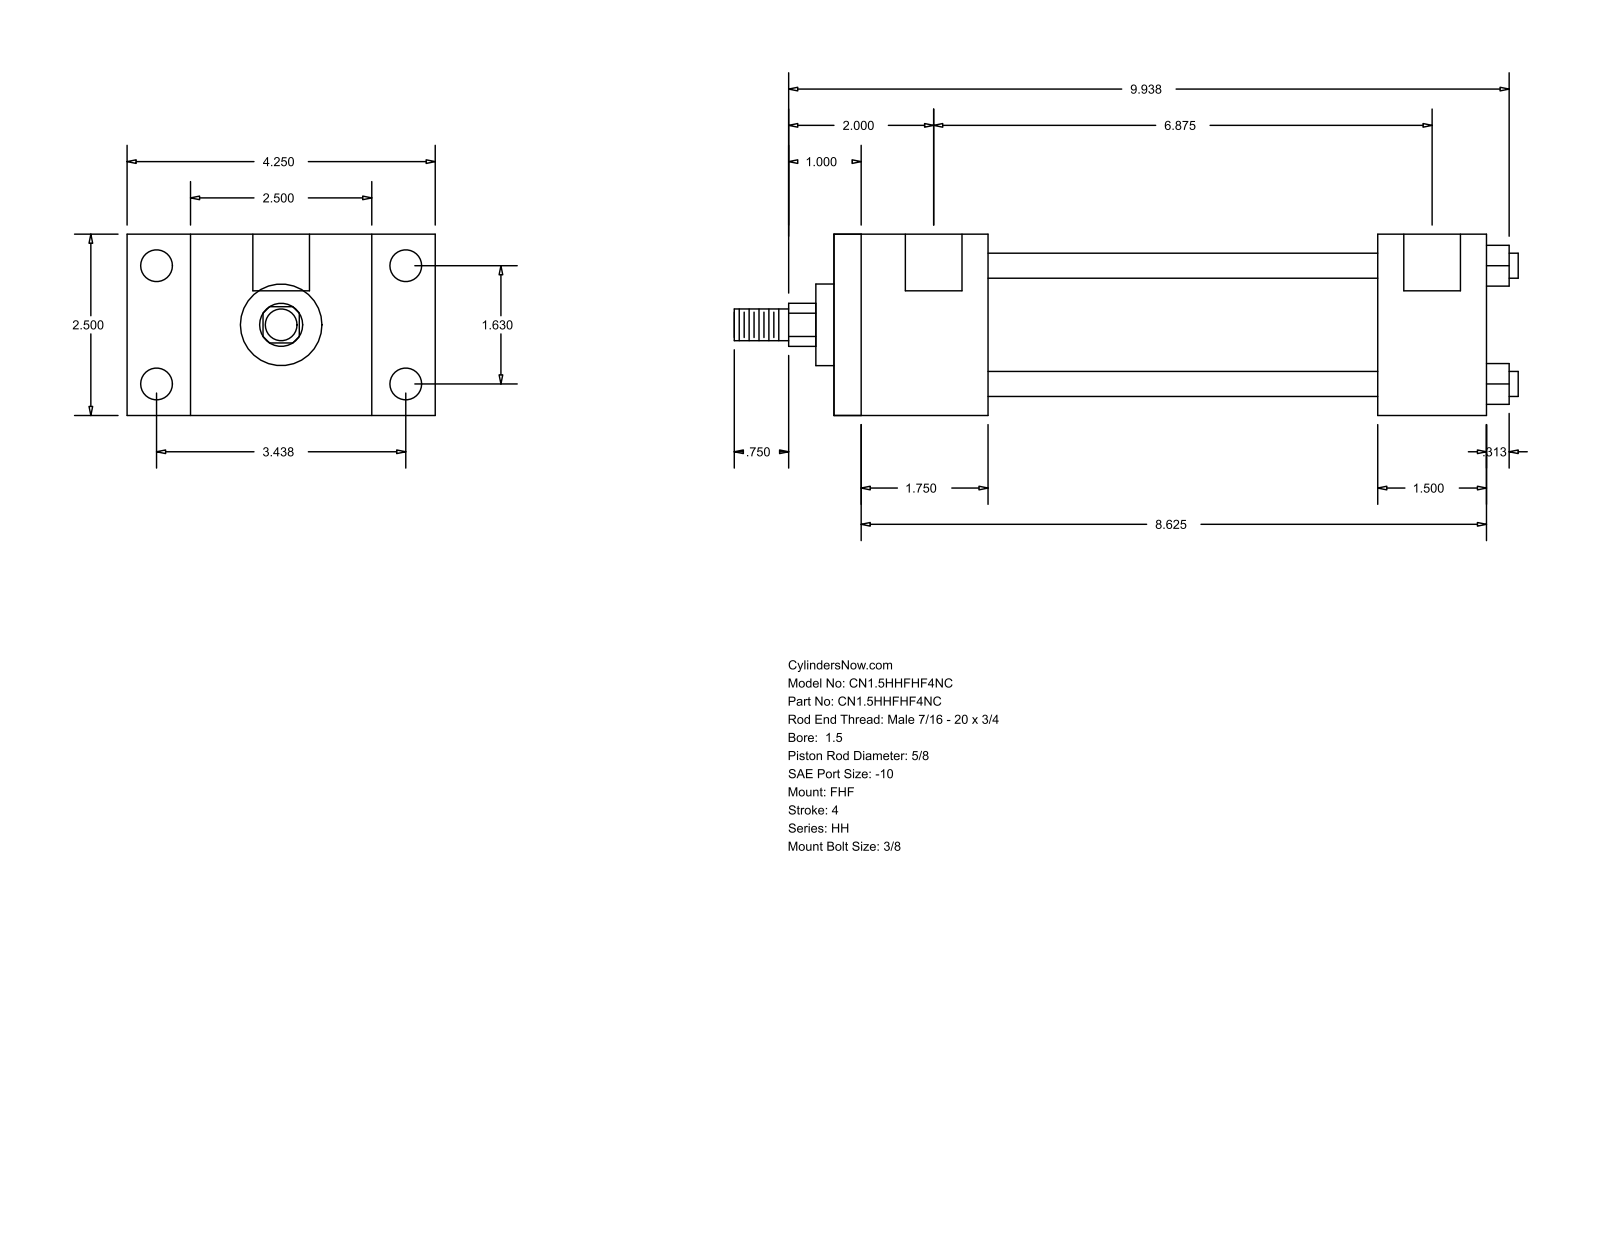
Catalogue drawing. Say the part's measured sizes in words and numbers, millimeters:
The part is named "HH_FHF__0150_0.625". Its 3-D file was written by "GSSL Pune (CONFIG_CONTROL_DESIGN)". It is 0 solids with 88 faces: 60 planar, 28 cylindrical and 0 other. Overall it measures 274.64 by 107.95 by 63.5 millimeters. Round holes: 4 of diameter 5.56, 4 of diameter 11.13, 2 of diameter 19.84. Round bosses or shafts: 4 of diameter 8.76, 1 of diameter 44.45, 1 of diameter 28.57, 1 of diameter 15.88, 1 of diameter 11.11. Partial cylindrical surfaces (rounded edges, fillets, slot ends): 1 of radius 7.54. The main face-to-face distances are 63.5, 22.23, 85.73, 53.97, 107.96, 228.59, 174.62, 190.5, 136.53, 38.09. The hole center spacings are 41.4, 87.32, 96.64, 177.8, 1.58, 1.59, 174.63, 176.21.
